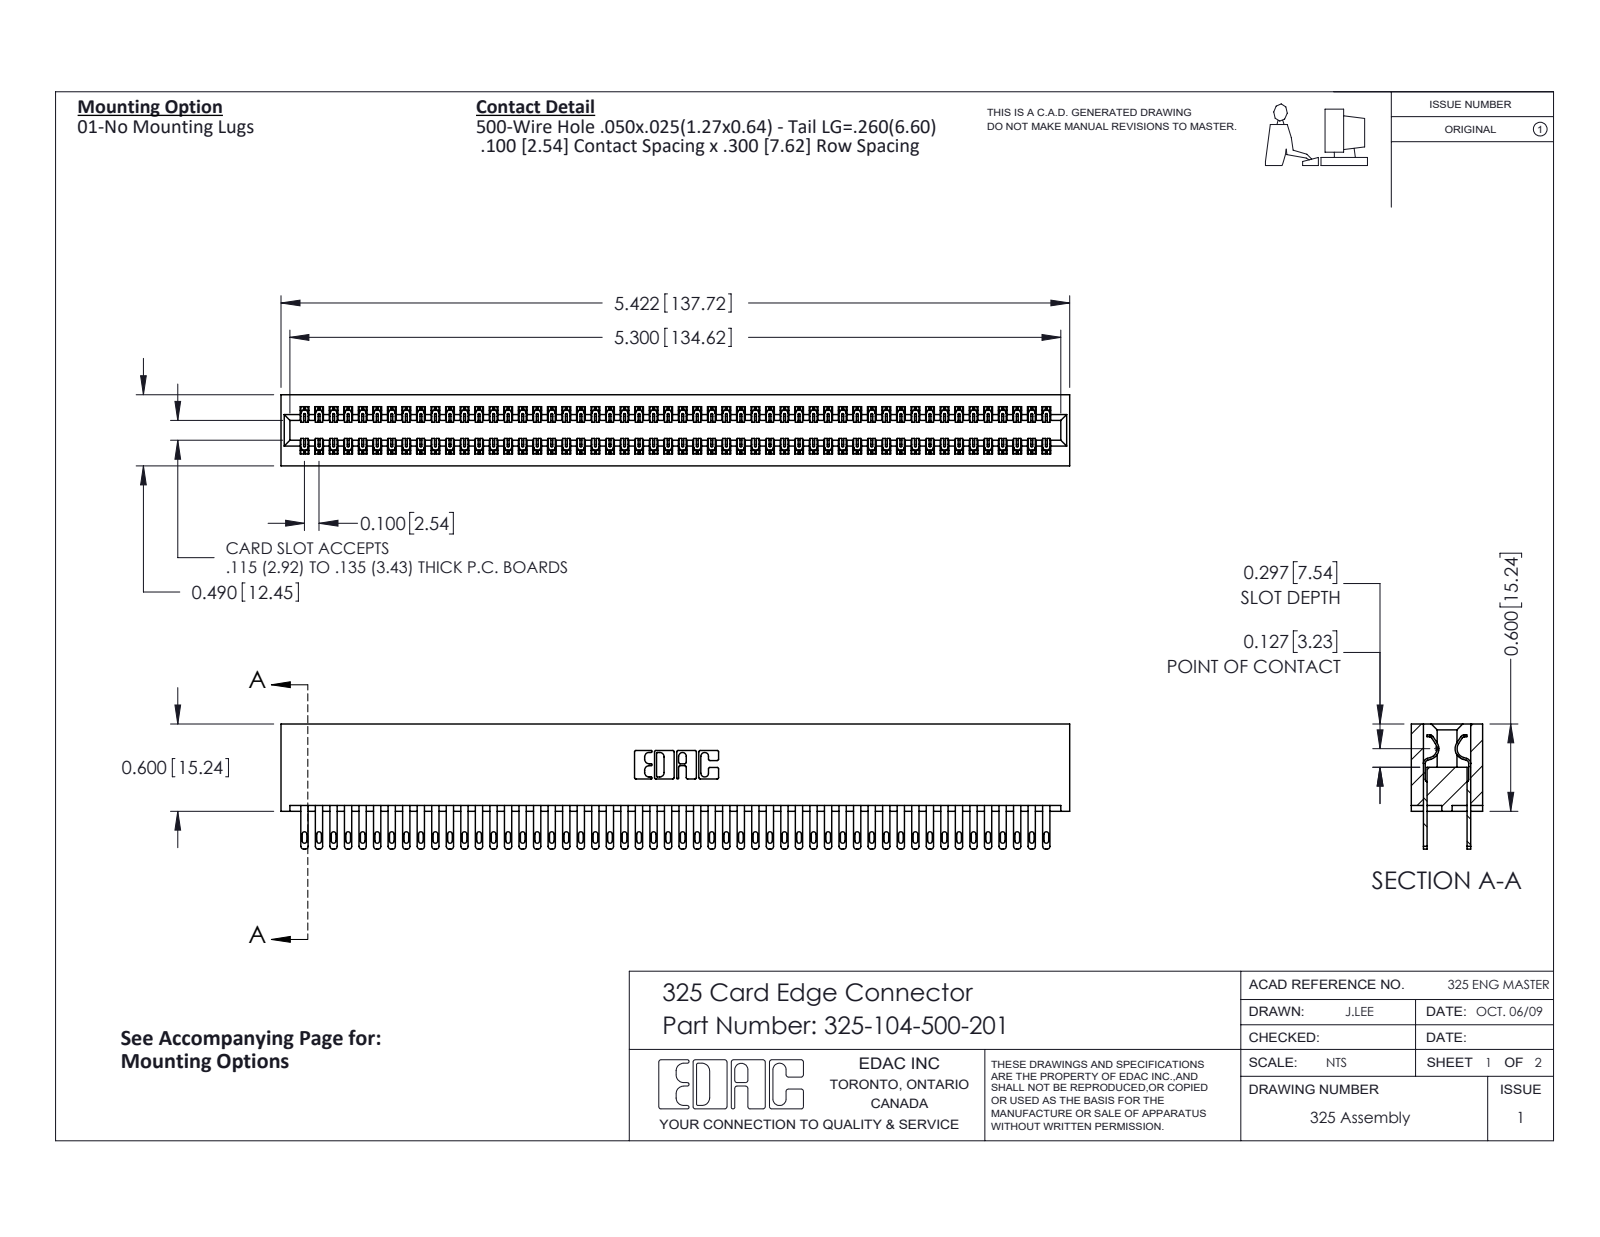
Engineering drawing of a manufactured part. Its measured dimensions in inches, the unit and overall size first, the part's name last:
Units: inches
Overall size (bounding box): 5.422 × 0.86 × 0.49
Partial cylindrical surfaces — rounded edges, fillets, slot ends (radius × count): R0.006 ×156, R0.016 ×104, R0.02 ×104, R0.01 ×22, R0.007 ×6, R0.031 ×6, R0.026 ×3, R0.014 ×2
Main face-to-face distances: 0.083, 0.407, 0.3, 0.107, 0.383, 0.025, 0.325, 0.49, 0.275, 0.56
Volume: 1.147 in³ · Surface area: 38.33 in²
Bodies: 105 solids, 5098 faces (3186 planar, 1912 cylindrical, 0 other)
Part name (STEP PRODUCT): 325-104-500-201; 325-292-001_325-293-100; 325 Part_Lugless
STEP written by: SolidWorks 2016 (CONFIG_CONTROL_DESIGN)
